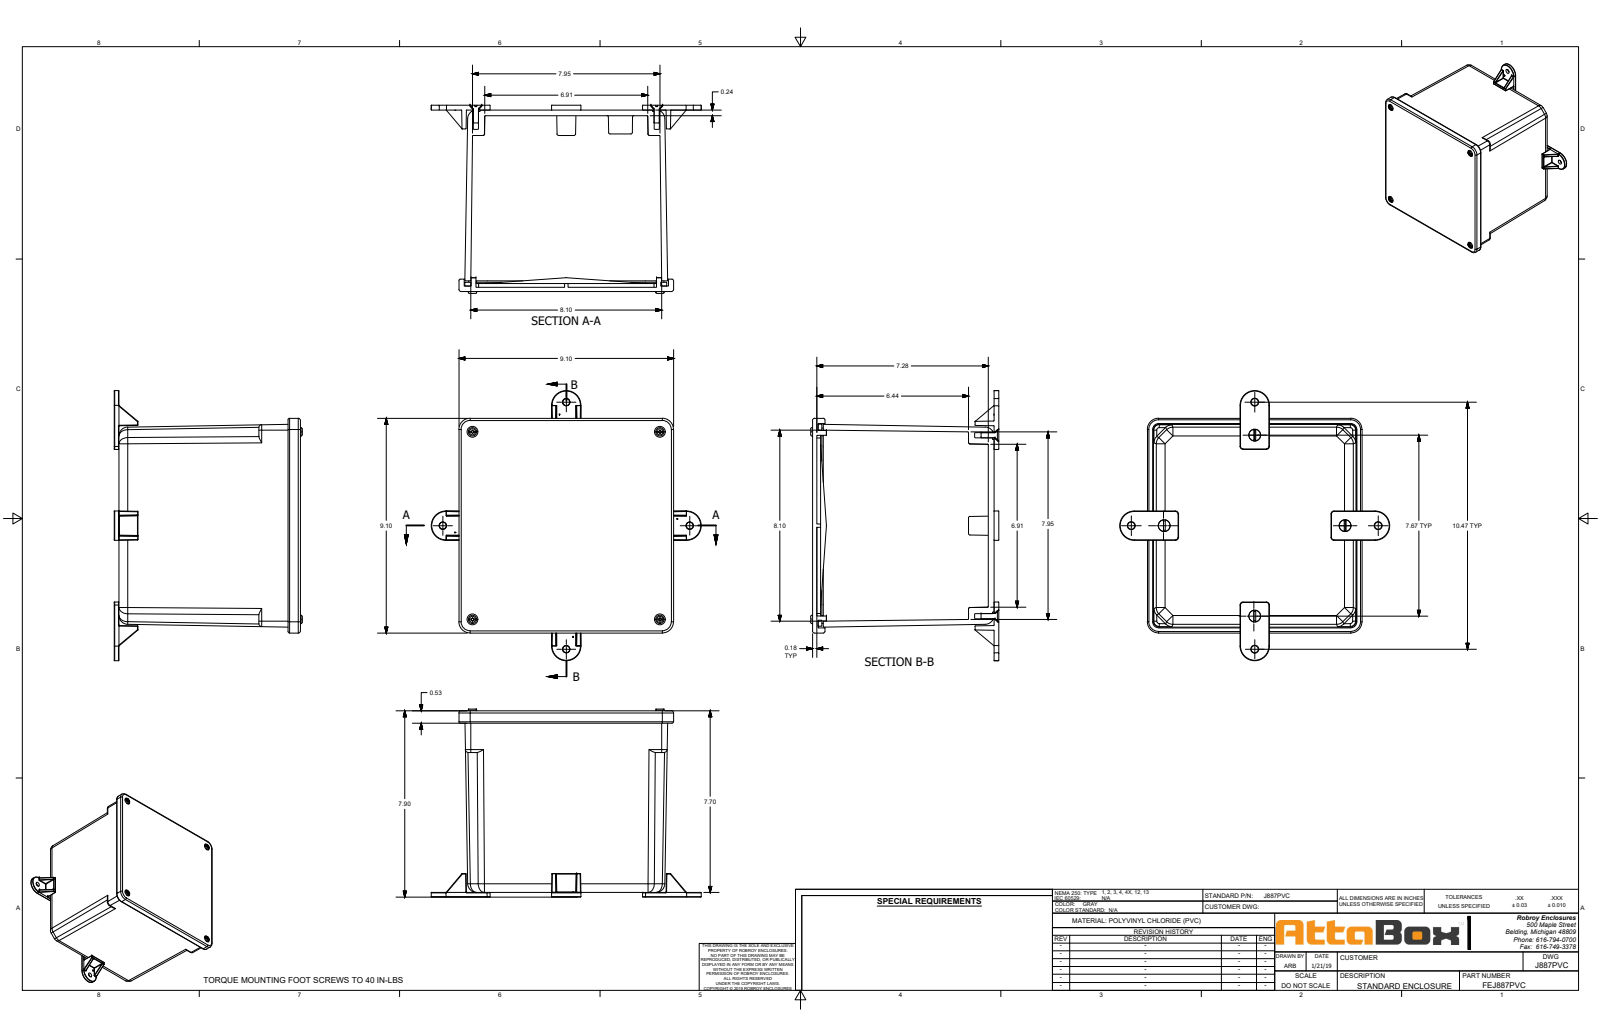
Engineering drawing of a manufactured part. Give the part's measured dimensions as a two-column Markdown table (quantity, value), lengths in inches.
| quantity | value |
| --- | --- |
| part name | J887PVC |
| STEP written by | SolidWorks 2018 (AUTOMOTIVE_DESIGN) |
| units | inches |
| bodies | 23 solids, 1020 faces (467 planar, 324 cylindrical, 229 other) |
| overall size | 11.45 × 11.45 × 7.973 |
| volume | 96.64 in³ |
| surface area | 888.3 in² |
| round holes (diameter × count) | 0.265 × 8, 0.13 × 4, 0.2 × 4, 0.22 × 4, 0.276 × 4, 0.32 × 4, 0.35 × 4, 0.39 × 4, 0.465 × 4, 0.495 × 4, 0.5 × 4 |
| round bosses / shafts (diameter × count) | 0.354 × 4, 0.224 × 4, 0.187 × 4, 0.177 × 4, 0.325 × 3, 0.325 × 1 |
| partial cylindrical surfaces (radius × count) | 0.02 × 76, 0.125 × 28, 0.005 × 16, 0.375 × 16, 0.03 × 12, 0.094 × 12, 0.25 × 10, 0.063 × 6 |
| main face-to-face distances | 7.697, 0.18, 0.24, 7.517, 7.457, 7.277, 7.462, 7.222, 0.055, 0.235 |
| hole center spacings | 7.95, 3.978, 7.906, 8.763, 3.977, 7.95, 8.763, 0.044 |
